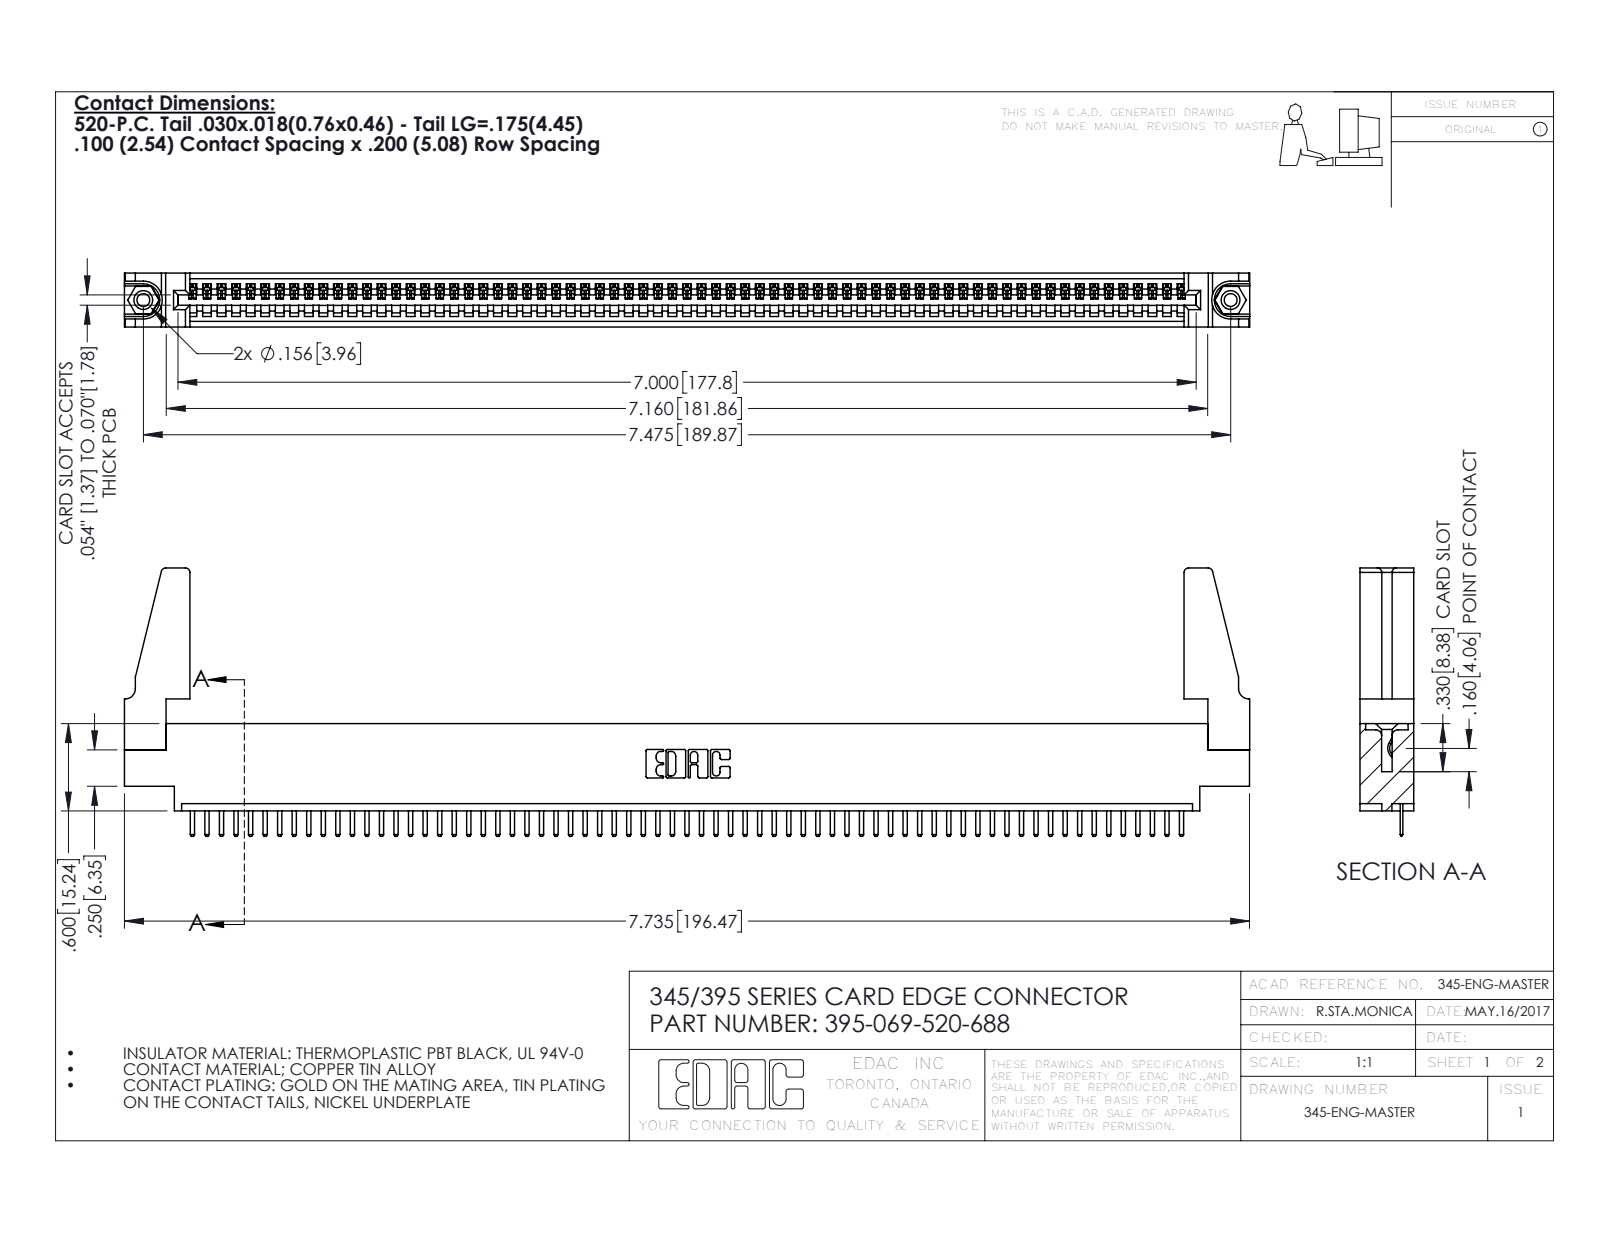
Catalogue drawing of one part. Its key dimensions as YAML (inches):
part_name: "345-220-078_345-220-088; 345-250-001_345-250-001-102; 345 Part_0.170 Offset - 0.156 Dia-TH; 395-069-520-688 (+1 more)"
step_written_by: "SolidWorks 2016 (CONFIG_CONTROL_DESIGN)"
units: inches
bodies: {solids: 74, faces: 4532, planar: 3054, cylindrical: 1462, other: 16}
overall_size: [7.736, 1.845, 0.37]
volume: 1.332
surface_area: 42.86
round_holes:
  - {diameter: 0.089, count: 2}
  - {diameter: 0.125, count: 2}
  - {diameter: 0.156, count: 2}
  - {diameter: 0.064, count: 1}
round_bosses_or_shafts:
  - {diameter: 0.155, count: 2}
partial_cylinders:
  - {radius: 0.01, count: 140}
  - {radius: 0.006, count: 138}
  - {radius: 0.01, count: 22}
  - {radius: 0.03, count: 8}
  - {radius: 0.007, count: 6}
  - {radius: 0.031, count: 6}
  - {radius: 0.026, count: 3}
  - {radius: 0.031, count: 2}
face_to_face_distances: [0.072, 0.298, 0.37, 0.098, 0.272, 0.025, 0.2, 0.225, 0.072, 0.175]
hole_center_spacings: [0.27, 7.239, 7.475]
